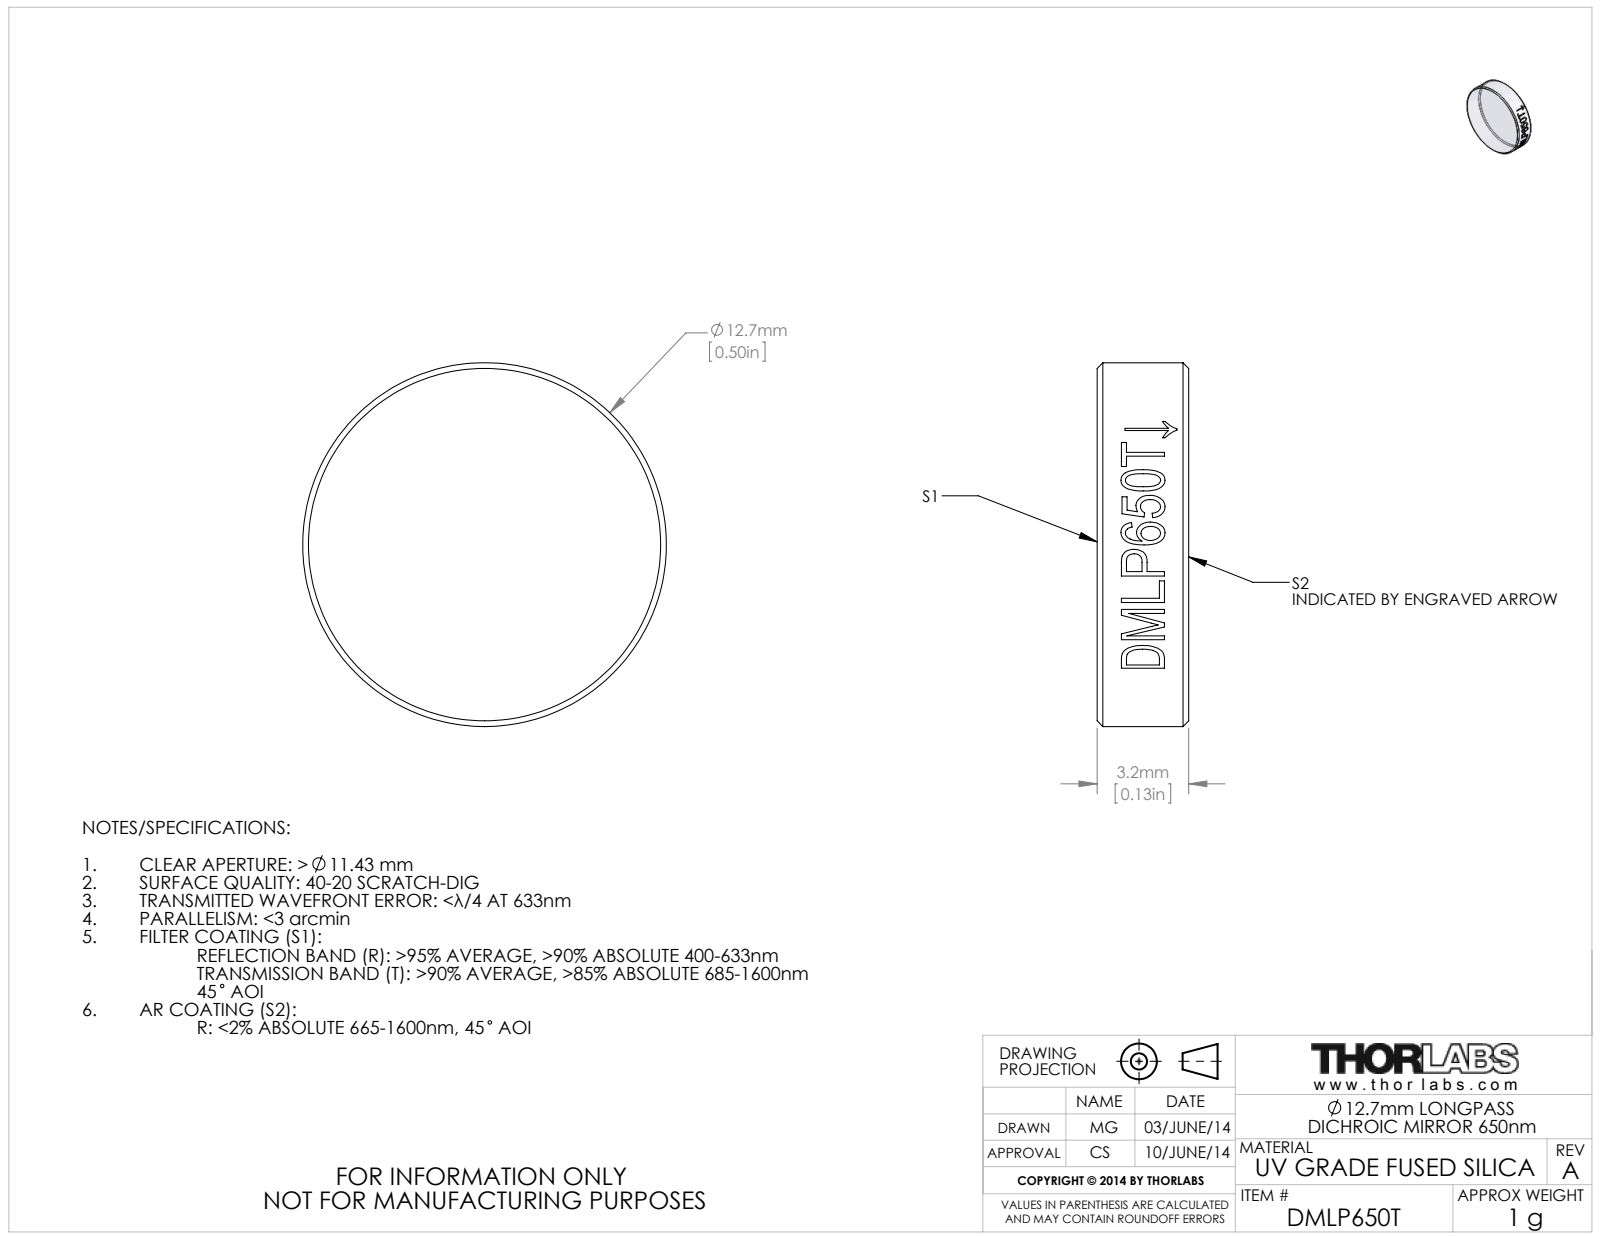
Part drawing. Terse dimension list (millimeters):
name: TTN028291-E0W
written by: SolidWorks 2012 (CONFIG_CONTROL_DESIGN)
unit: mm
bodies: 1 solid, 21 faces (2 planar, 15 cylindrical, 4 other)
size: 12.7 × 12.7 × 3.2
volume: 404 mm³; area: 372 mm²
bosses: 1× ⌀12.7
face distances: 3.2
